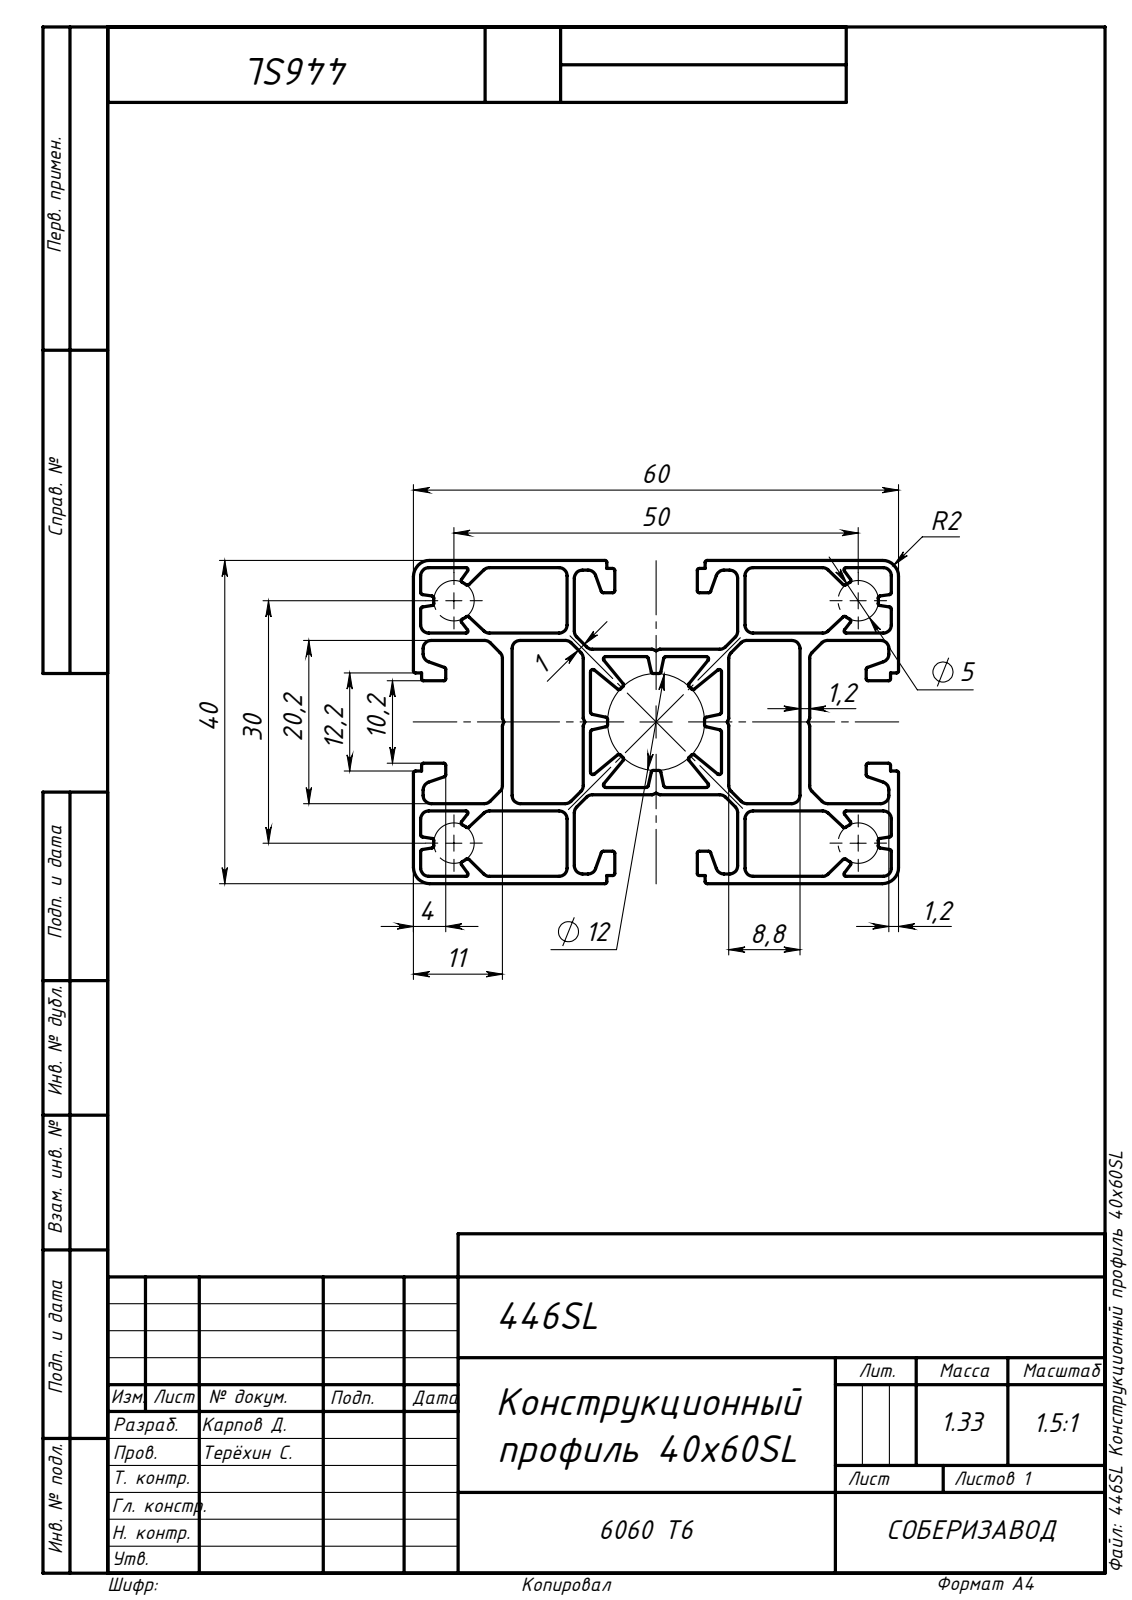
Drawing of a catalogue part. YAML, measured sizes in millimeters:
step_written_by: "SolidWorks 2018 (AUTOMOTIVE_DESIGN)"
units: millimeters
bodies: {solids: 1, faces: 416, planar: 192, cylindrical: 224, other: 0}
overall_size: [1000, 60, 40]
volume: 493569
surface_area: 840511
partial_cylinders:
  - {radius: 0.25, count: 100}
  - {radius: 1, count: 68}
  - {radius: 0.3, count: 24}
  - {radius: 2, count: 4}
  - {radius: 2.5, count: 4}
face_to_face_distances: [0.9, 30.1, 9, 19.1, 2, 11, 21.1, 1.1, 20, 39.1]
